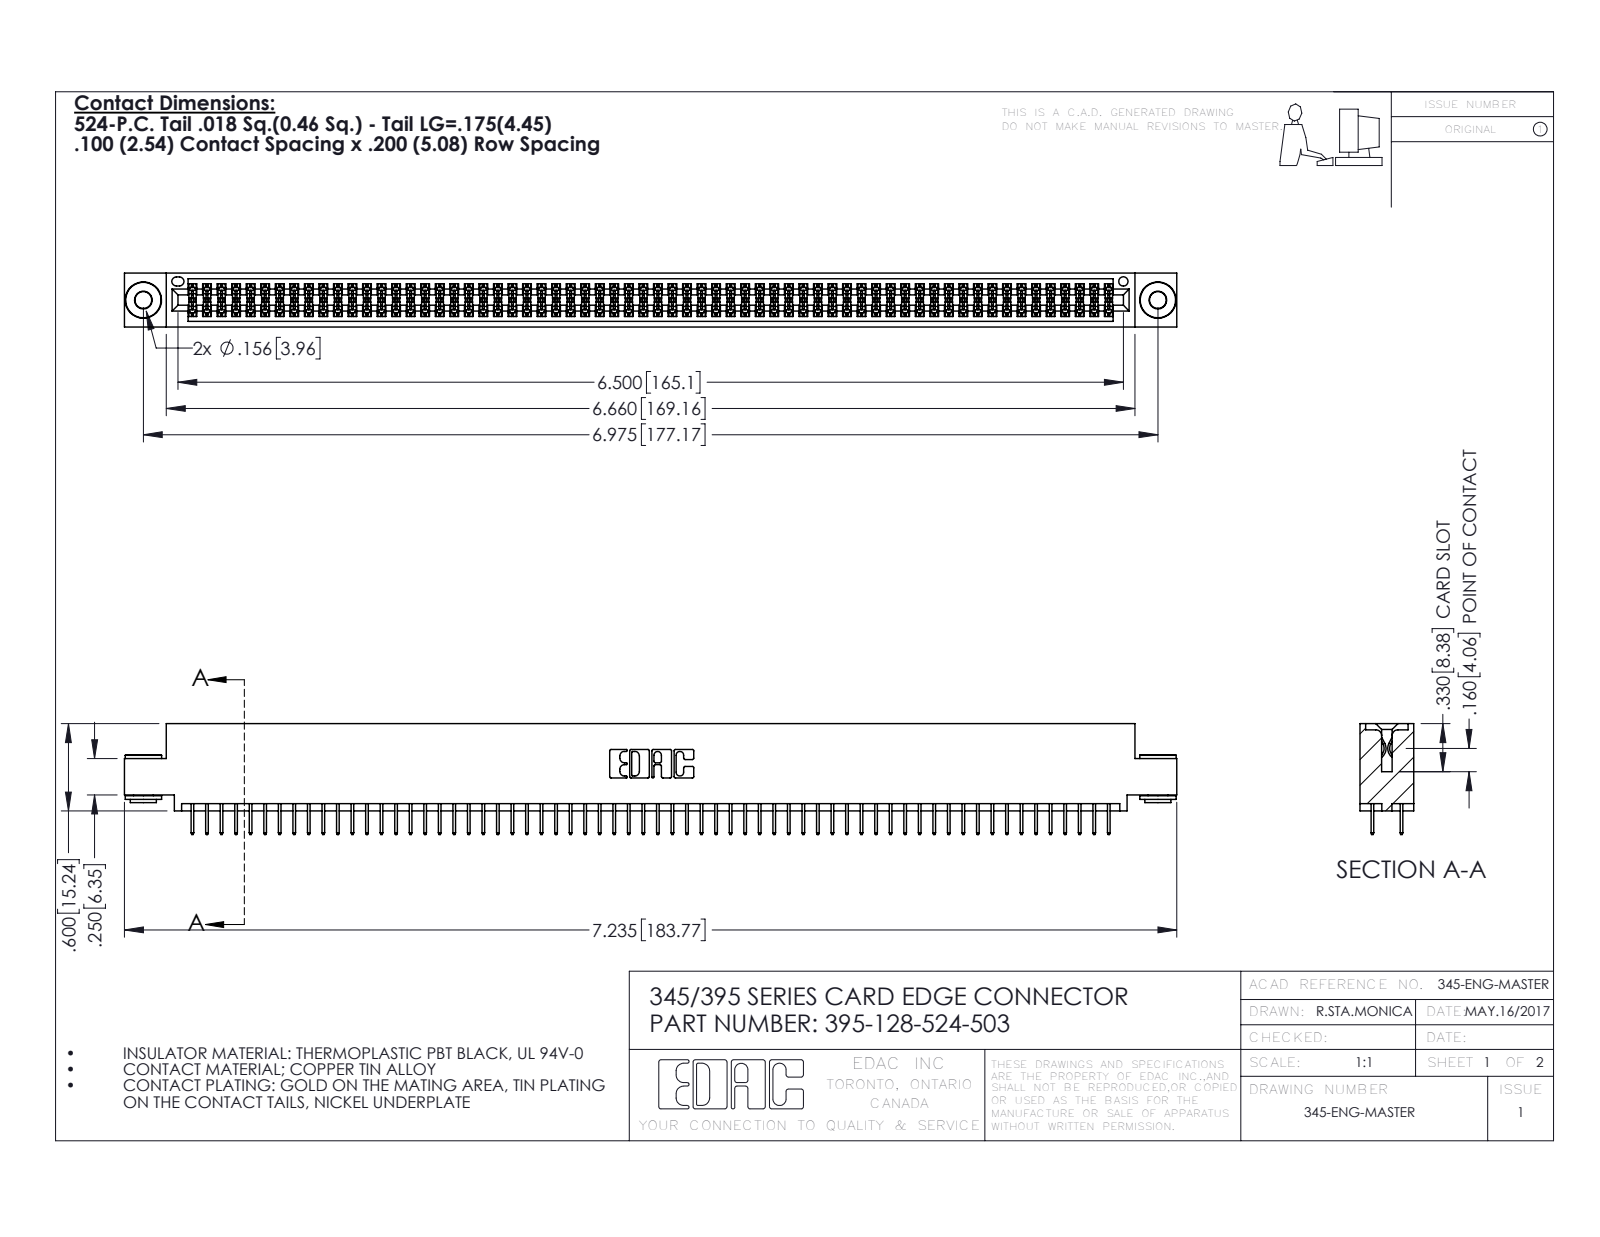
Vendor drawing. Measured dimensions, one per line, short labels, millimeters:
name: 345-250-002_345-250-002-102; 345-292-001_345-293-124; 395-128-524-503; 345 Part_0.110 Offset - 0.156 Dia-TH
written by: SolidWorks 2016 (CONFIG_CONTROL_DESIGN)
unit: mm
bodies: 131 solids, 7080 faces (5086 planar, 1986 cylindrical, 8 other)
size: 183.8 × 19.4 × 9.4
volume: 17 810 mm³; area: 26 540 mm²
holes: 2× ⌀2.9, 2× ⌀4, 1× ⌀1.6
bosses: 2× ⌀6.4, 2× ⌀4.6, 2× ⌀3.5
rounds: 192× R0.2, 22× R0.3, 6× R0.2, 6× R0.8, 3× R0.7, 2× R0.4, 2× R0.5, 2× R0.6
face distances: 1.8, 7.6, 5.1, 9.4, 0.6, 2.5, 6.9, 5.7, 1.8, 4.4
hole spacings: 6.9, 171.2, 177.2
